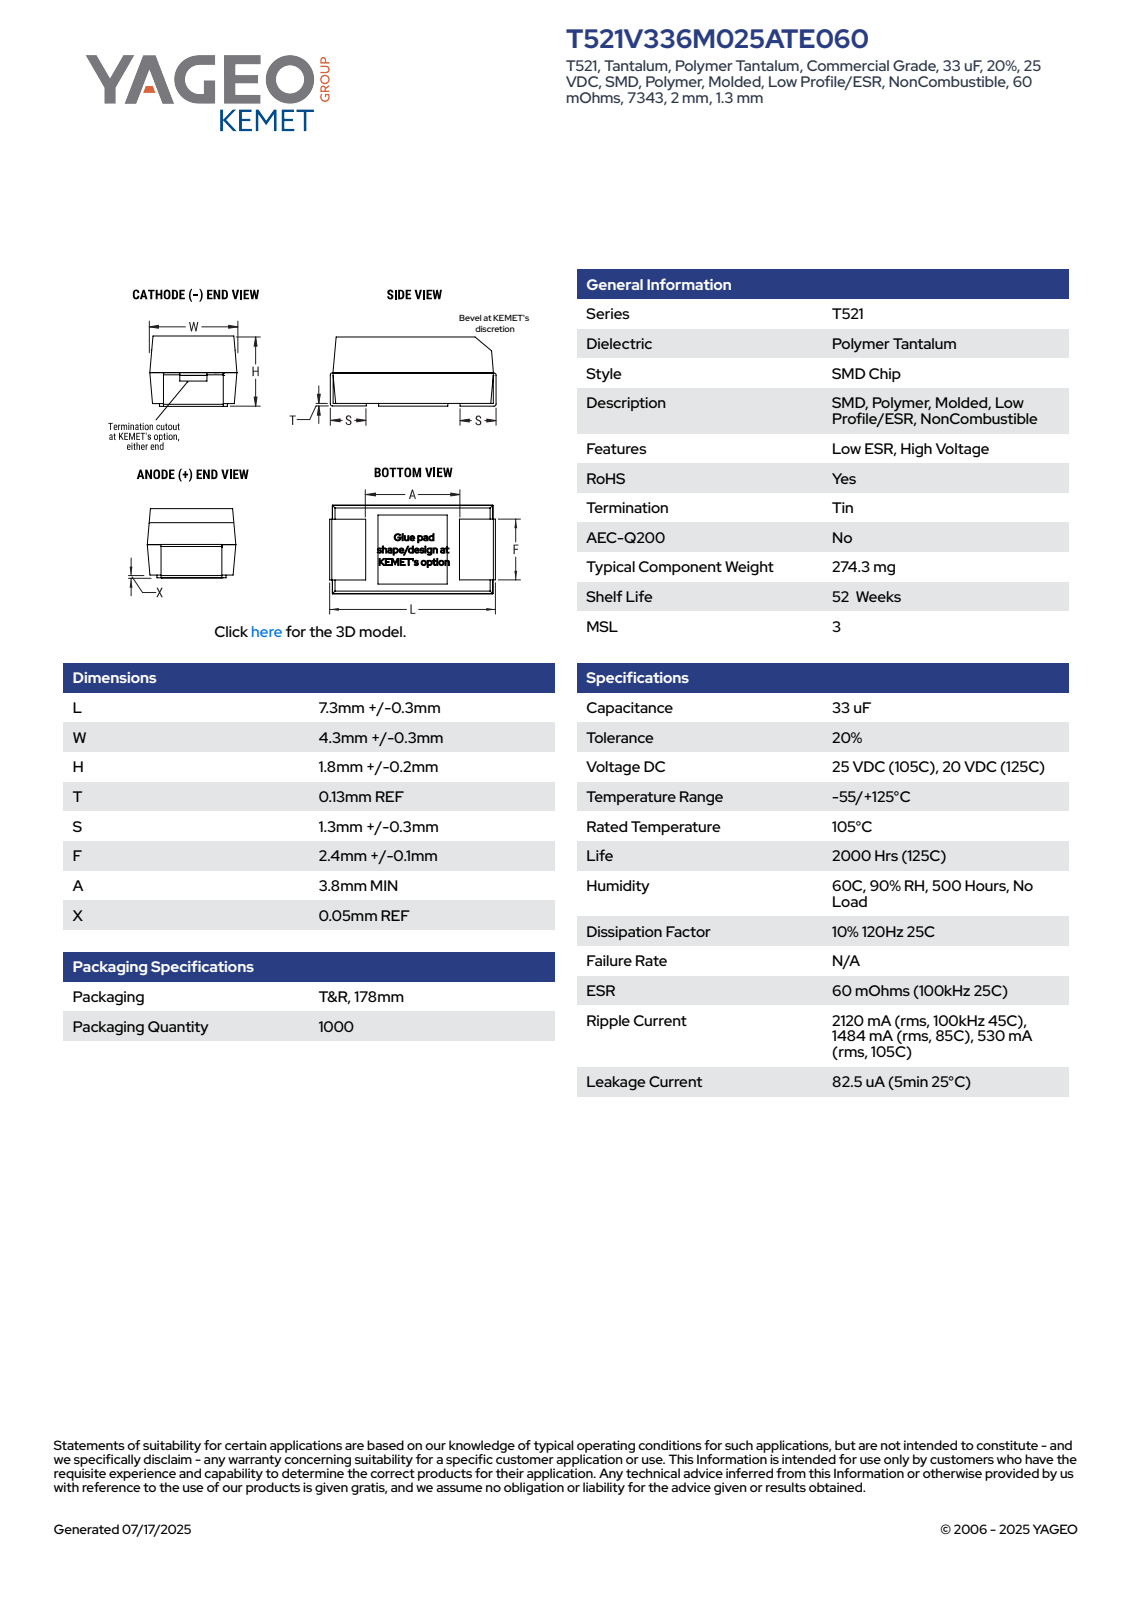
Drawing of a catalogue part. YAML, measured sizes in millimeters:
part_name: "CTSM_TCM2NBKRPEG_7343_L7.6W4.6H2T0.13S1.3F2.5A3.6X0.05"
step_written_by: "SolidWorks 2014 (AUTOMOTIVE_DESIGN)"
units: millimeters
bodies: {solids: 4, faces: 90, planar: 86, cylindrical: 4, other: 0}
overall_size: [7.6, 4.6, 2.13]
volume: 62
surface_area: 117
partial_cylinders:
  - {radius: 0.1, count: 4}
face_to_face_distances: [2, 4.45, 4.44, 2.13, 7.47, 7.6, 7.34, 1.3, 6.3, 1.17]
